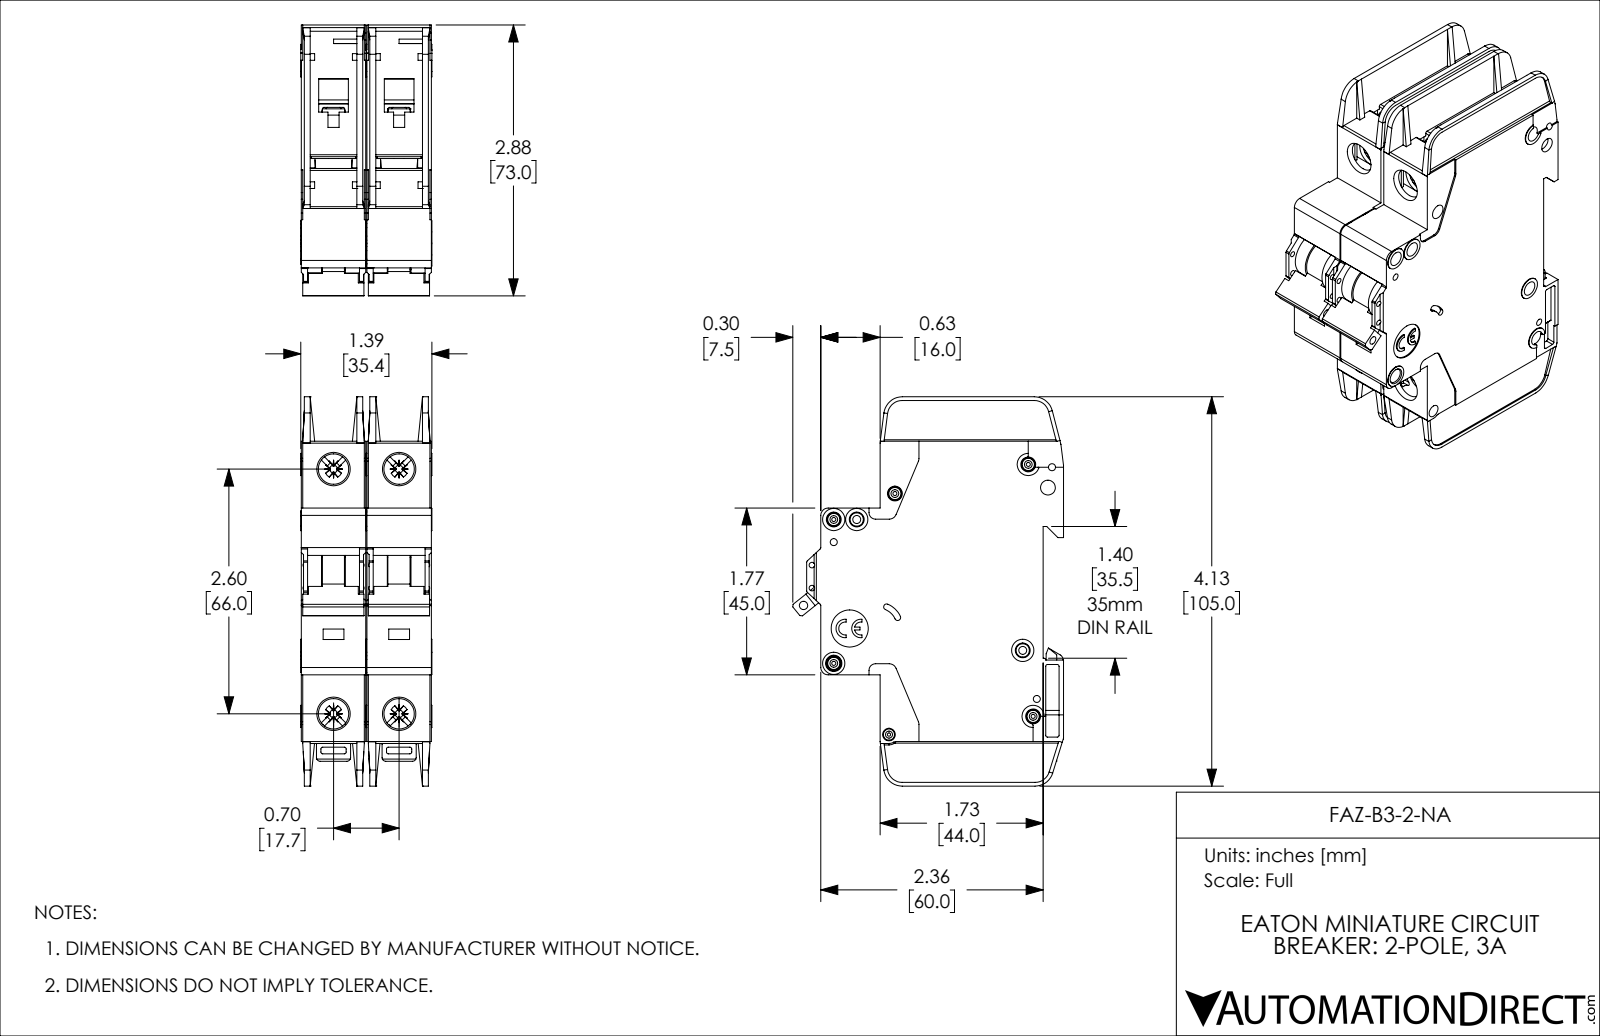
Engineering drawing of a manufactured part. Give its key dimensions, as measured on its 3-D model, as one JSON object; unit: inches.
{"part_name": "FAZ-B3-2-NA", "step_written_by": "SolidWorks 2019 (AUTOMOTIVE_DESIGN)", "units": "inches", "bodies": {"solids": 2, "faces": 2254, "planar": 1342, "cylindrical": 714, "other": 198}, "overall_size": [4.134, 2.876, 1.394], "volume_in3": 9.365, "surface_area_in2": 82.01, "round_holes": [[0.157, 8], [0.043, 5], [0.075, 4], [0.323, 4], [0.059, 2], [0.085, 2], [0.035, 1], [0.089, 1], [0.098, 1], [0.134, 1], [0.394, 1]], "round_bosses_or_shafts": [[0.13, 5], [0.236, 4], [0.118, 3], [0.098, 2]], "partial_cylinders_radius": [[0.02, 57], [0.016, 20], [0.039, 14], [0.079, 10], [0.043, 8], [0.008, 5], [0.197, 5], [0.01, 4]], "face_to_face_distances": [0.697, 0.047, 0.685, 0.591, 0.094, 0.638, 0.543, 1.382, 0.744, 0.65], "hole_center_spacings": [0.244, 0.537, 0.697, 0.87, 2.598, 2.69, 0.189, 0.199]}
